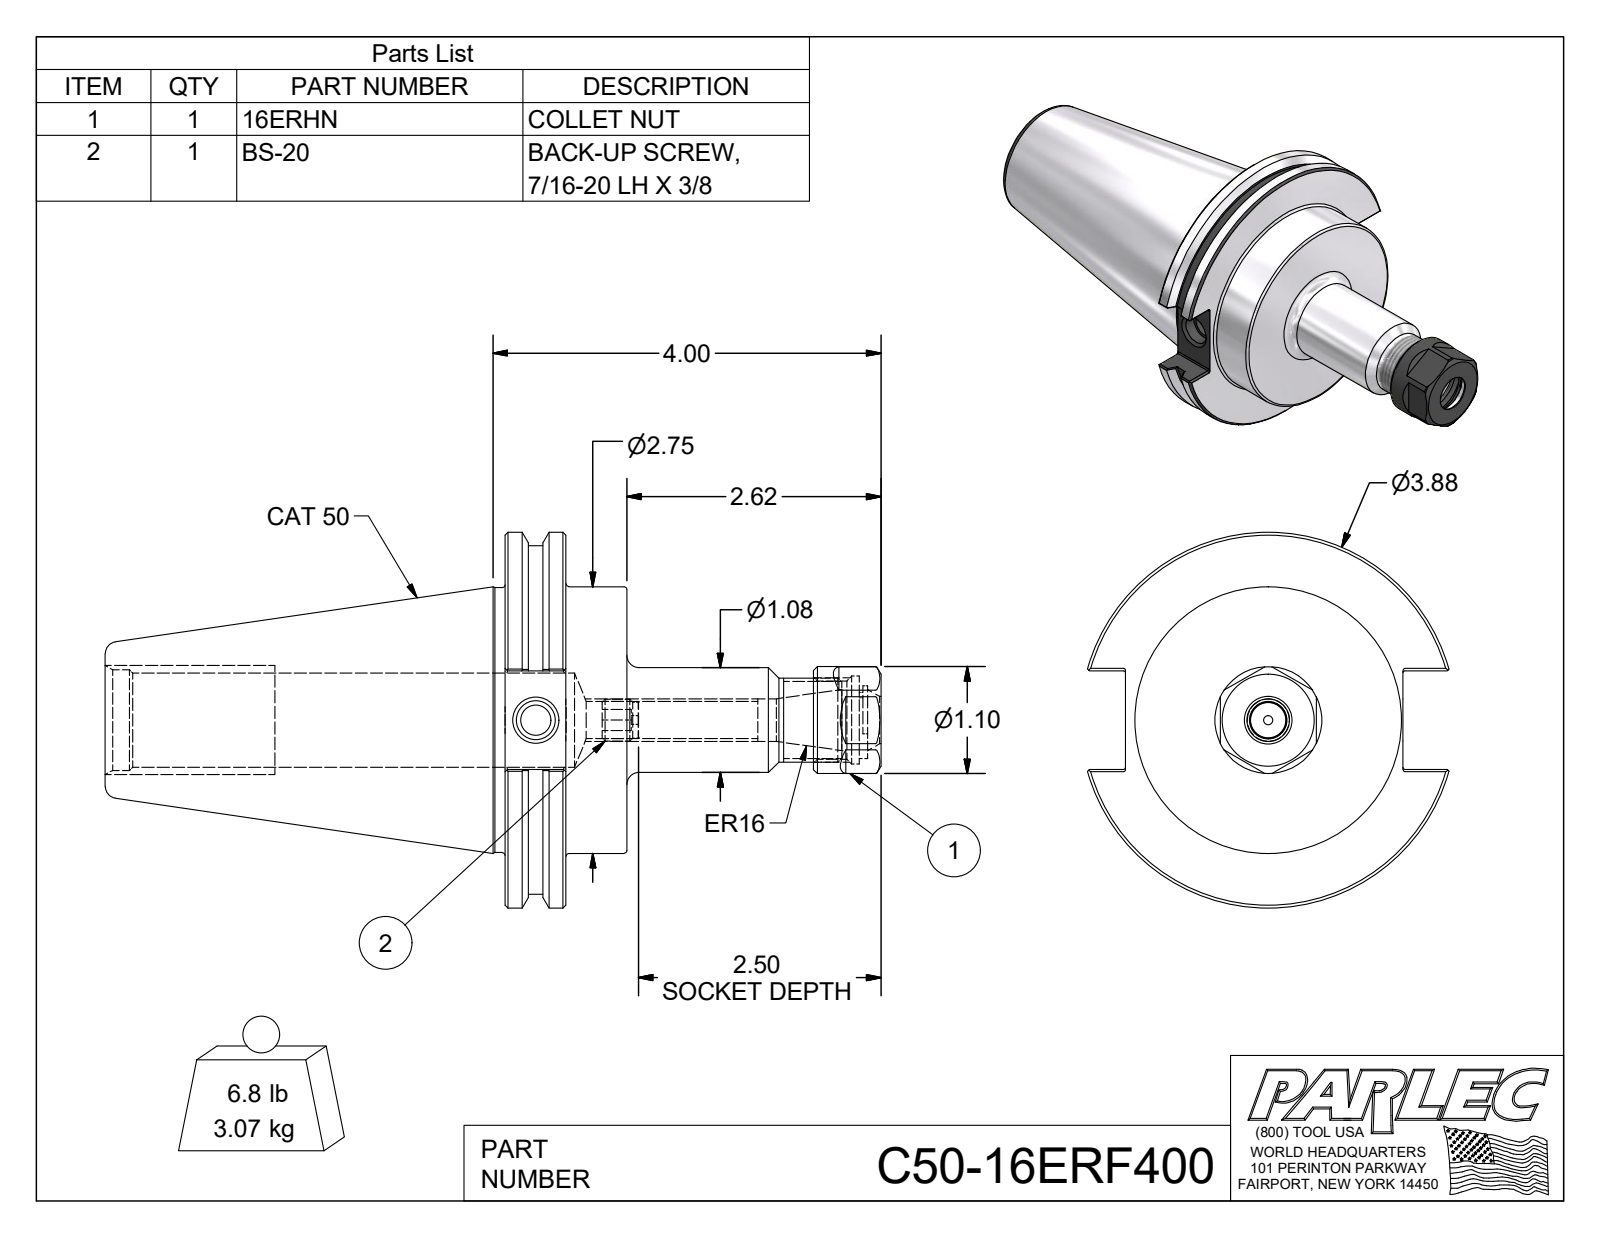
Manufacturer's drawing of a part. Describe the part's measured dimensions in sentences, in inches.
The part is named "C50-16ER4-1; 16ERHN; BS-20; C50-16ERF400". Its 3-D file was written by "Autodesk Inventor 2016 (AUTOMOTIVE_DESIGN)". It is 3 solids with 143 faces: 59 planar, 38 cylindrical and 46 other. Overall it measures 8 by 3.875 by 3.729 inches. Its volume is 24.08 cubic inches and its surface area 92.55 square inches. Round holes: 1 of diameter 0.09, 1 of diameter 0.315, 1 of diameter 0.383, 1 of diameter 0.399, 1 of diameter 0.44, 1 of diameter 0.488, 1 of diameter 0.67, 1 of diameter 0.807, 1 of diameter 0.906, 1 of diameter 0.97, 1 of diameter 1.038. Round bosses or shafts: 1 of diameter 3.875, 1 of diameter 3.594, 1 of diameter 2.75, 1 of diameter 2.73, 1 of diameter 1.102, 1 of diameter 1.08, 1 of diameter 0.866, 1 of diameter 0.432. Partial cylindrical surfaces (rounded edges, fillets, slot ends): 12 of radius 0.02, 1 of radius 0.285, 1 of radius 0.354. The main face-to-face distances are 1.255, 0.625, 0.63, 3.875, 3.25, 2.62, 0.99, 4.125, 4.75, 5.38. The hole center spacings are 0.06.
